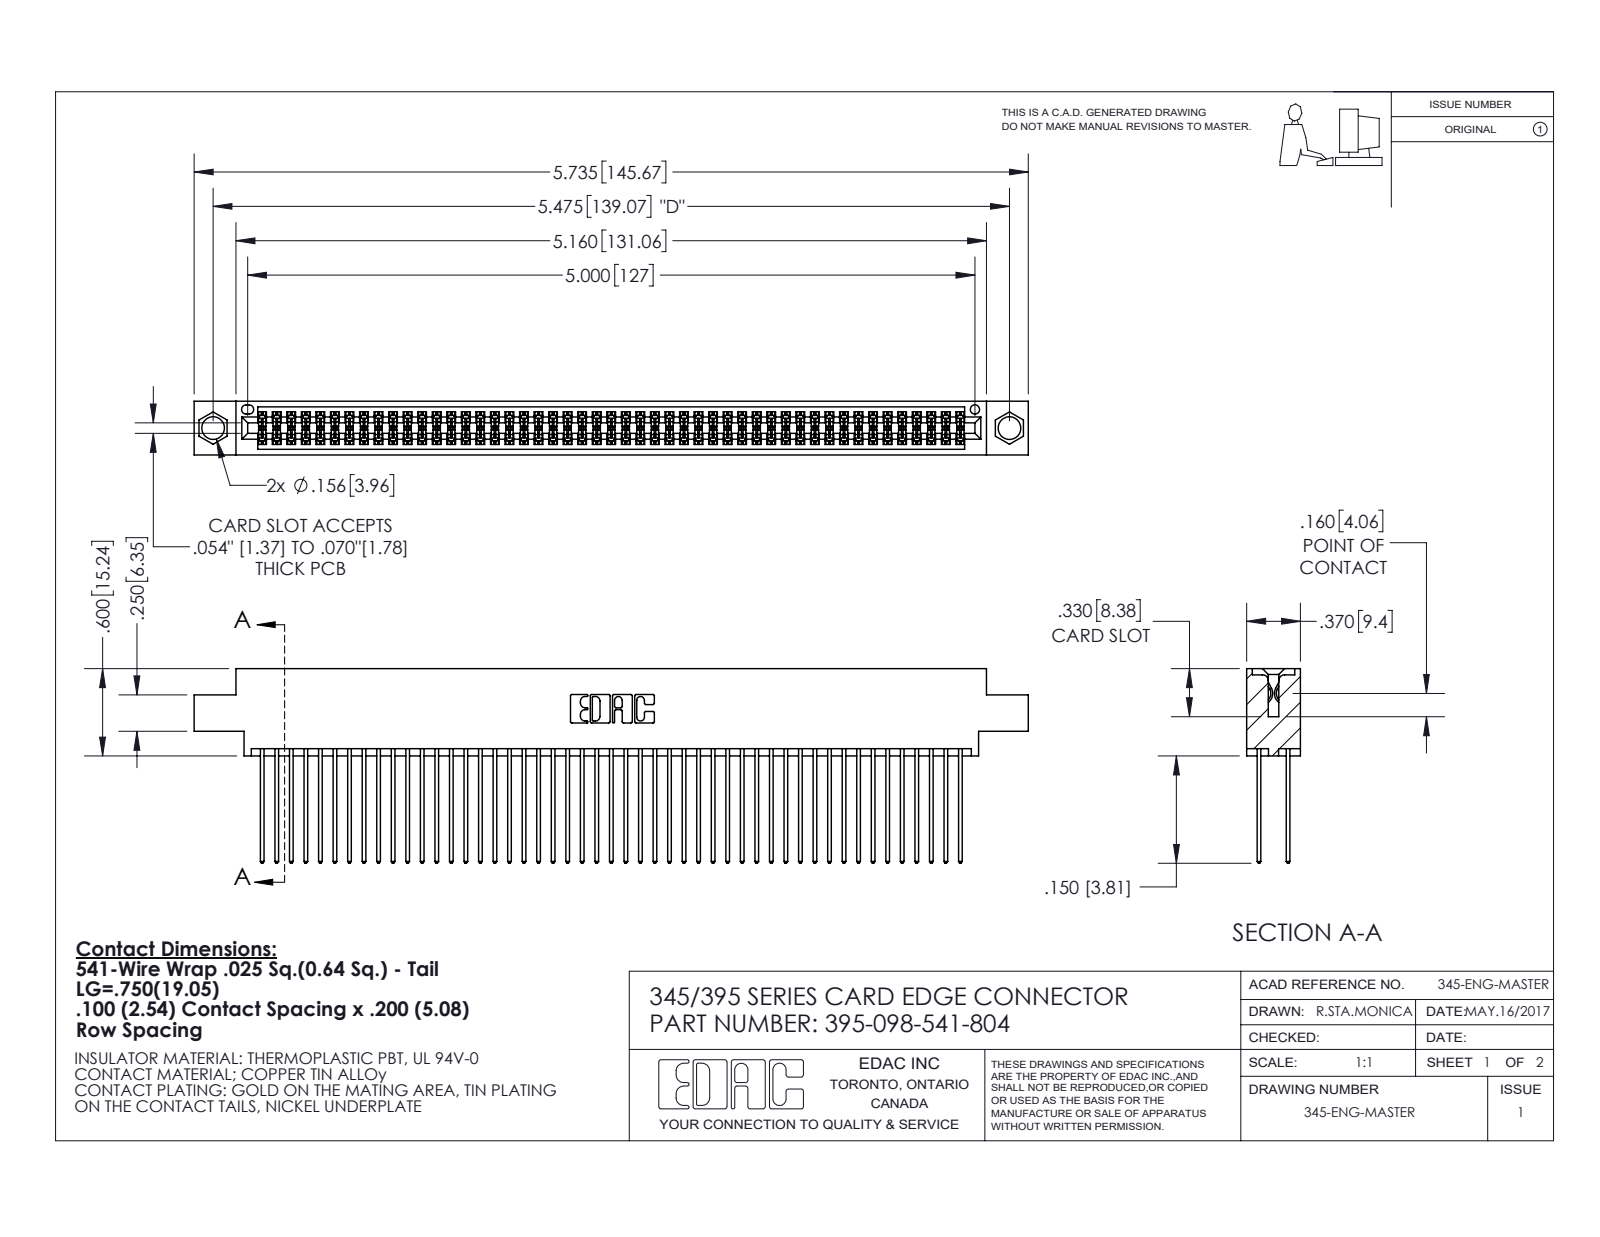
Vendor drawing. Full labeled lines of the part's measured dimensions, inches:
Part name (STEP PRODUCT): 345-292-001_345-293-141; 345 Part_0.170 Offset - 0.156 Dia-TI; 395-098-541-804
STEP written by: SolidWorks 2020 (CONFIG_CONTROL_DESIGN)
Units: inches
Bodies: 99 solids, 5044 faces (3332 planar, 1712 cylindrical, 0 other)
Overall size (bounding box): 5.735 × 1.337 × 0.37
Volume: 0.888 in³ · Surface area: 37.65 in²
Round holes (diameter × count): ⌀0.156 ×2, ⌀0.064 ×1
Partial cylindrical surfaces — rounded edges, fillets, slot ends (radius × count): R0.006 ×147, R0.01 ×98, R0.01 ×22, R0.007 ×6, R0.031 ×6, R0.026 ×3, R0.014 ×2, R0.019 ×2
Main face-to-face distances: 0.072, 0.298, 0.2, 0.098, 0.272, 0.025, 0.225, 0.37, 0.175, 0.149
Hole centre spacings: 0.27, 5.239, 5.475
